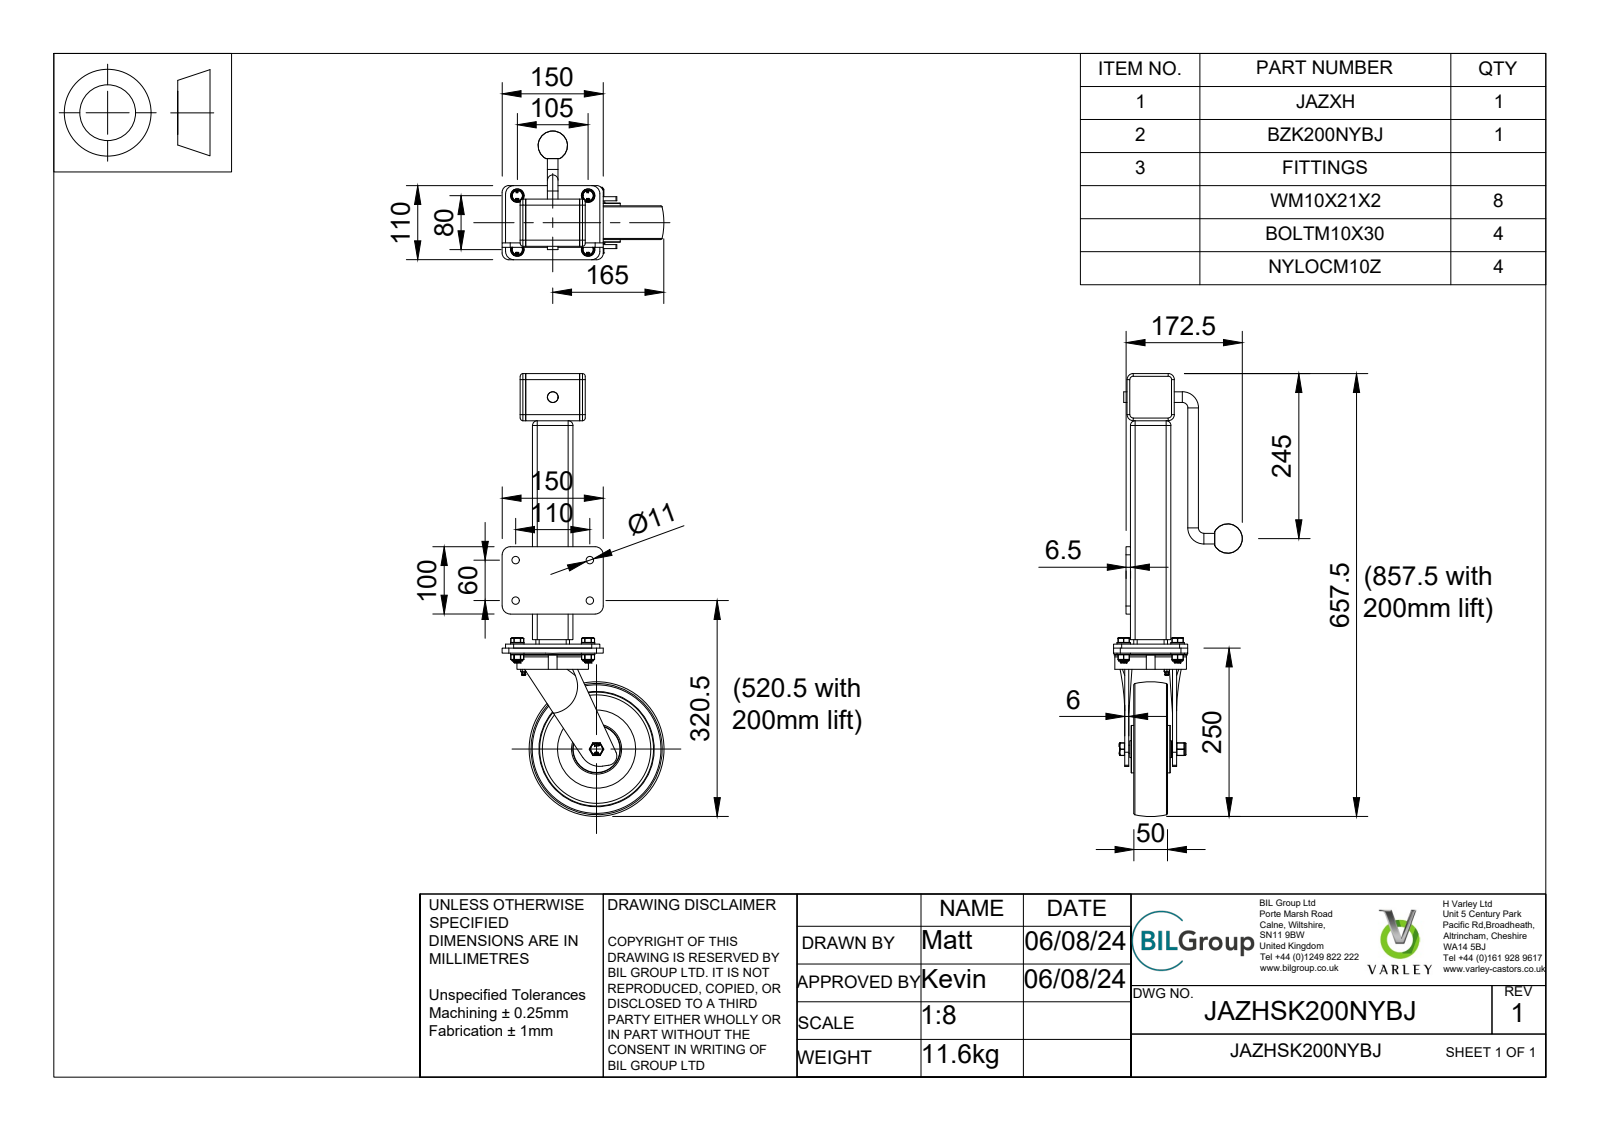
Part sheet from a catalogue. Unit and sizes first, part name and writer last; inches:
Units: inches
Overall size (bounding box): 25.886 × 9.449 × 7.52
Round holes (diameter × count): ⌀0.472 ×5, ⌀0.394 ×4, ⌀0.413 ×4, ⌀0.433 ×4, ⌀0.48 ×1, ⌀0.512 ×1, ⌀0.551 ×1, ⌀0.62 ×1, ⌀0.63 ×1, ⌀0.787 ×1, ⌀0.846 ×1, ⌀1.122 ×1
Round bosses / shafts (diameter × count): ⌀0.787 ×4, ⌀0.63 ×4, ⌀0.388 ×4, ⌀0.32 ×4, ⌀0.62 ×2, ⌀4.252 ×1, ⌀4.213 ×1, ⌀2.776 ×1
Partial cylindrical surfaces — rounded edges, fillets, slot ends (radius × count): R0.02 ×90, R0.013 ×16, R0.025 ×16, R0.025 ×8, R0.025 ×8, R0.138 ×8, R0.157 ×8, R0.191 ×8
Main face-to-face distances: 0.197, 0.118, 2.047, 2.244, 0.079, 0.315, 2.165, 1.85, 1.929, 2.362
Hole centre spacings: 2.598, 2.362, 2.505, 3.15, 4.134, 4.22, 4.331, 4.933
Volume: 135.4 in³ · Surface area: 1 122 in²
Bodies: 64 solids, 2103 faces (794 planar, 646 cylindrical, 663 other)
Part name (STEP PRODUCT): JAZHSK200NYBJ v3; BZK200AS v1; FABRICATED STEEL FORKS; FABRICATED STEEL FORKS Geometry (+8 more)
STEP written by: Autodesk Translation Framework v13.14.0.145 (AUTOMOTIVE_DESIGN)
